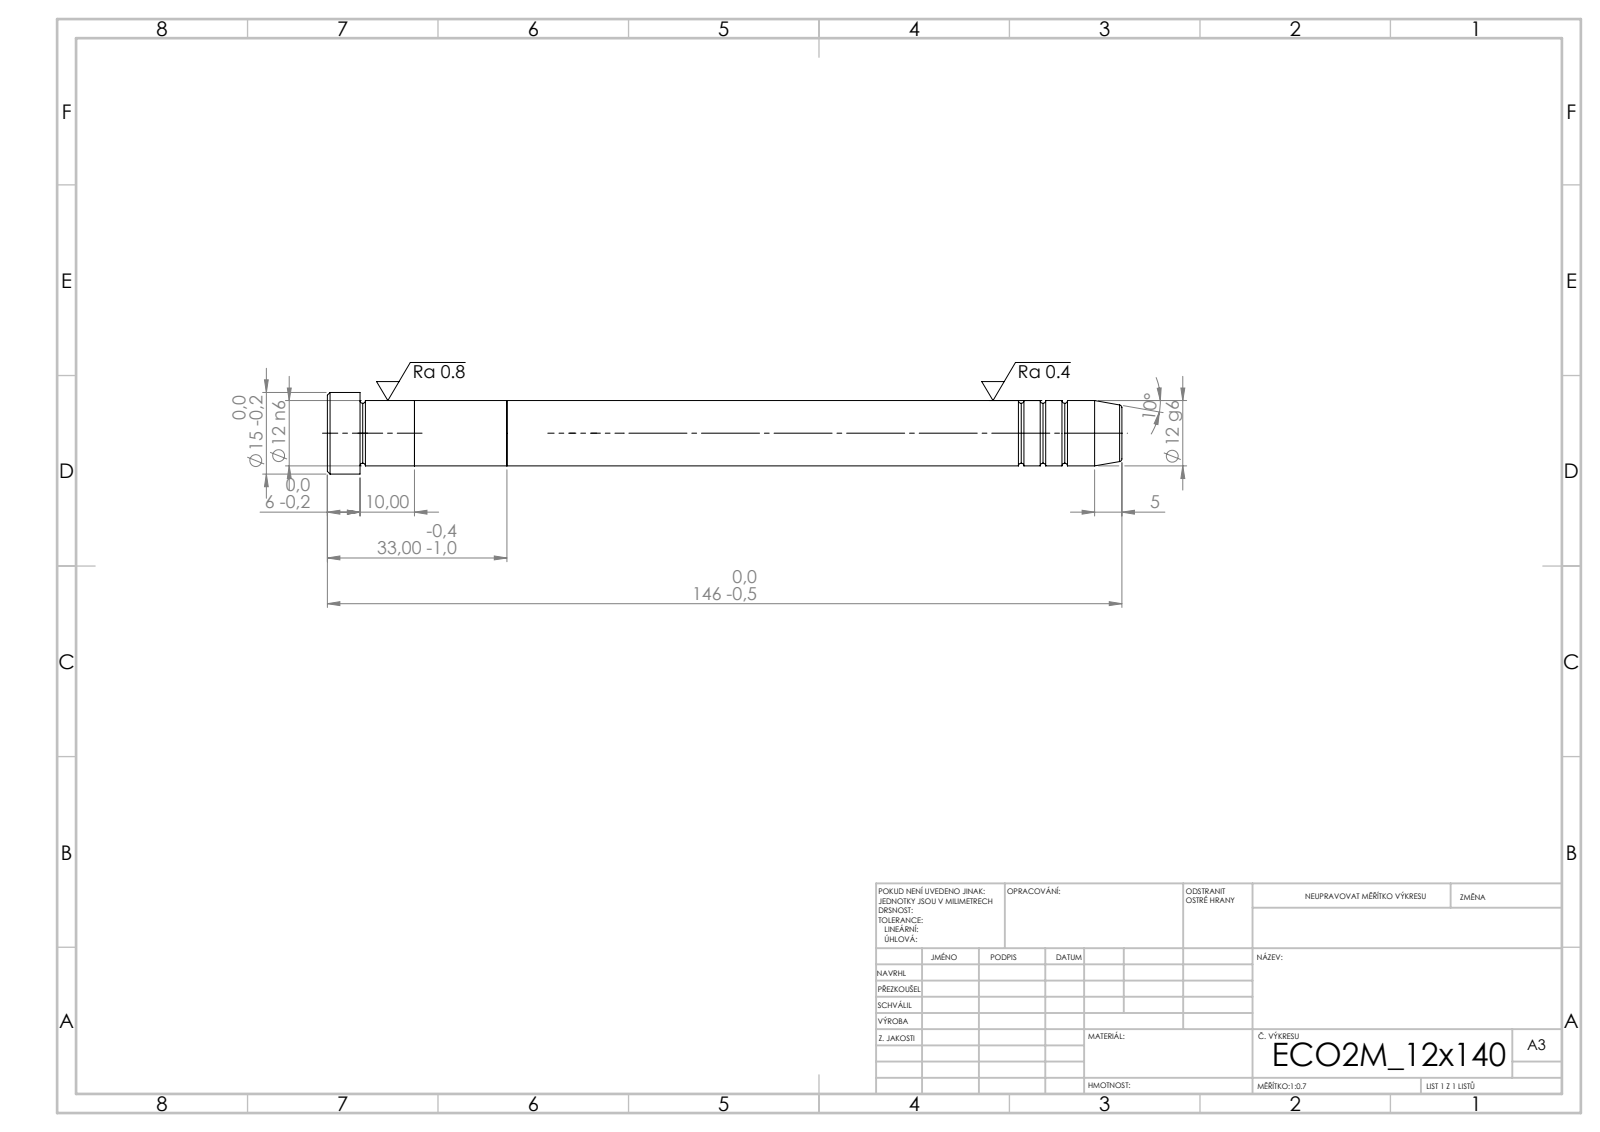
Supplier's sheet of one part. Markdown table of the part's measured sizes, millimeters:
| quantity | value |
| --- | --- |
| STEP written by | SolidWorks 2019 (CONFIG_CONTROL_DESIGN) |
| units | millimeters |
| bodies | 3 solids, 43 faces (7 planar, 14 cylindrical, 22 other) |
| overall size | 146 × 15 × 15 |
| volume | 16 751 mm³ |
| surface area | 6 379 mm² |
| round bosses / shafts (diameter × count) | 15 × 1, 12 × 1 |
| main face-to-face distances | 17, 33, 16, 113, 130, 146, 140, 27, 10, 6 |
